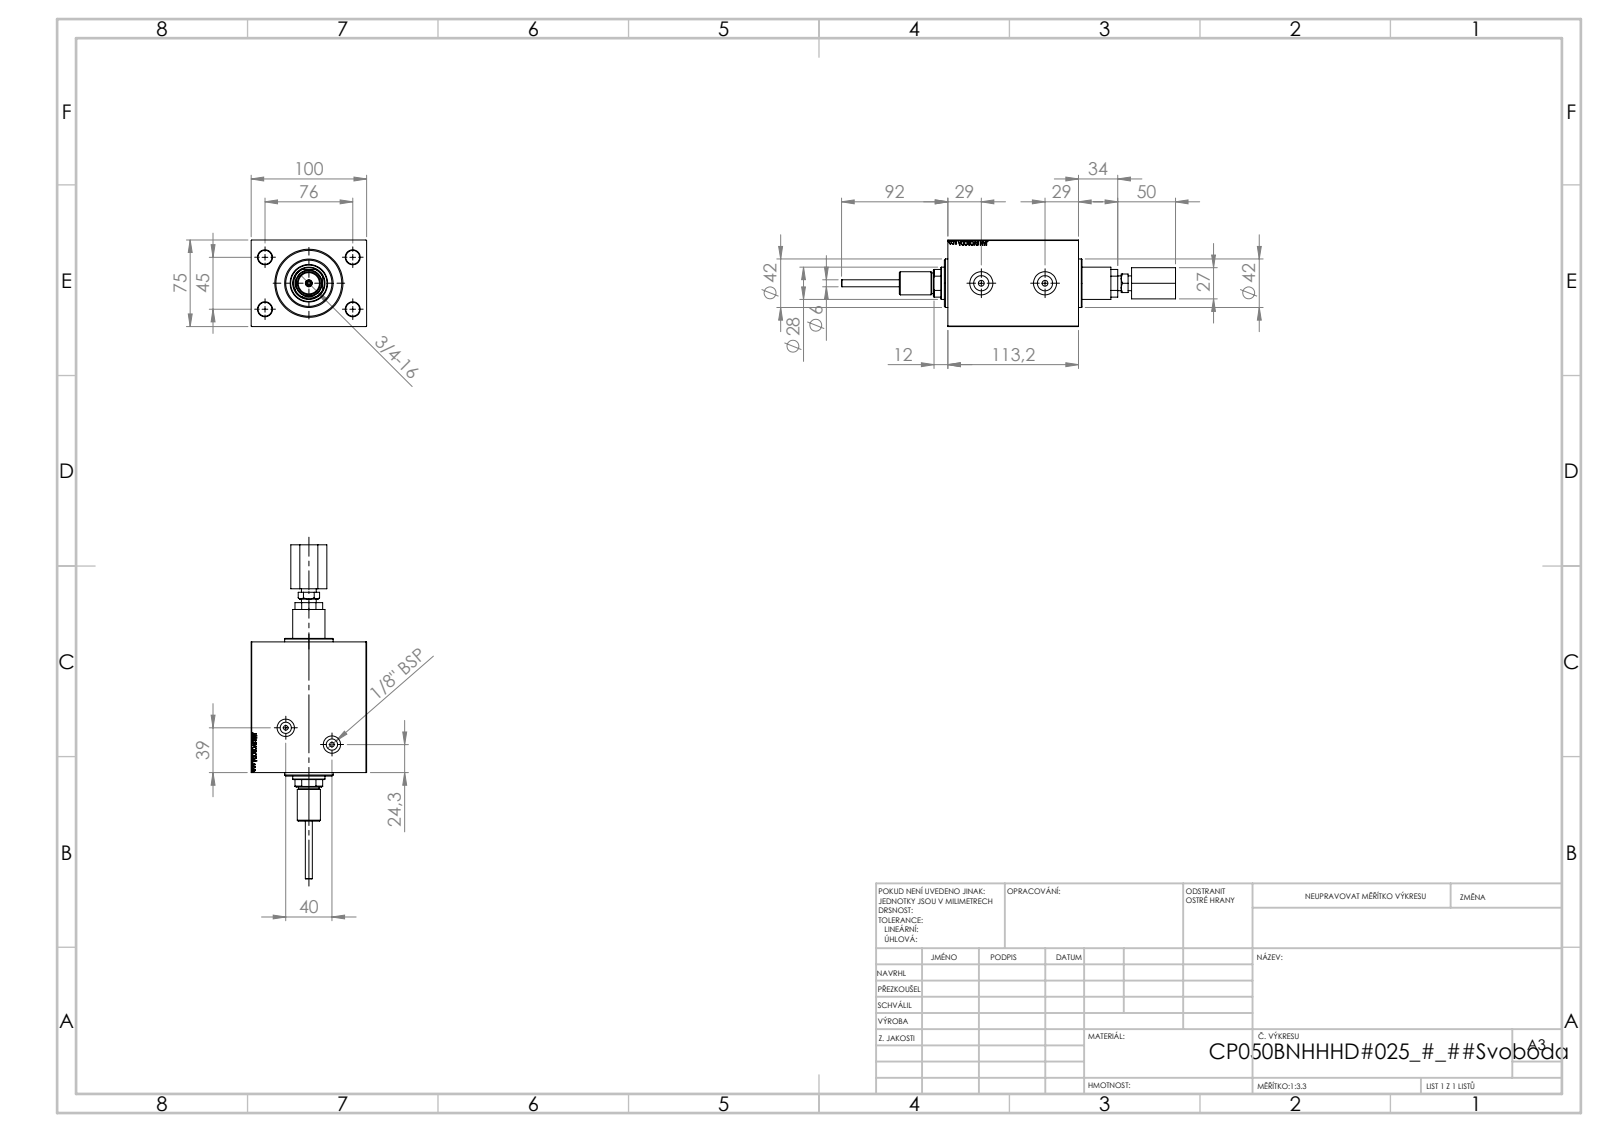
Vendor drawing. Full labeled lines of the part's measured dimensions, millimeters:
Part name (STEP PRODUCT): V450DCP_B_VCP; V450DCP_B_Body; V450DCP_VC_B; V450DCP_B_RodCooling_ACCESSORIES (+1 more)
STEP written by: SolidWorks 2019 (CONFIG_CONTROL_DESIGN)
Units: millimetres
Bodies: 5 solids, 986 faces (438 planar, 98 cylindrical, 450 other)
Overall size (bounding box): 289.2 × 100 × 75
Volume: 849 226 mm³ · Surface area: 132 636 mm²
Round holes (diameter × count): ⌀12 ×4, ⌀4 ×2, ⌀5 ×2, ⌀9.73 ×2, ⌀13.16 ×2, ⌀15 ×2, ⌀20 ×2, ⌀3 ×1, ⌀6 ×1, ⌀18.5 ×1, ⌀28 ×1, ⌀31.5 ×1
Round bosses / shafts (diameter × count): ⌀42 ×1, ⌀20 ×1, ⌀18 ×1, ⌀12.78 ×1
Partial cylindrical surfaces — rounded edges, fillets, slot ends (radius × count): R13.5 ×1
Main face-to-face distances: 75, 100, 113.2, 14, 99.2, 13, 43, 1, 27, 112.2
Hole centre spacings: 44.16, 45, 76, 88.32, 42.55, 55.2
